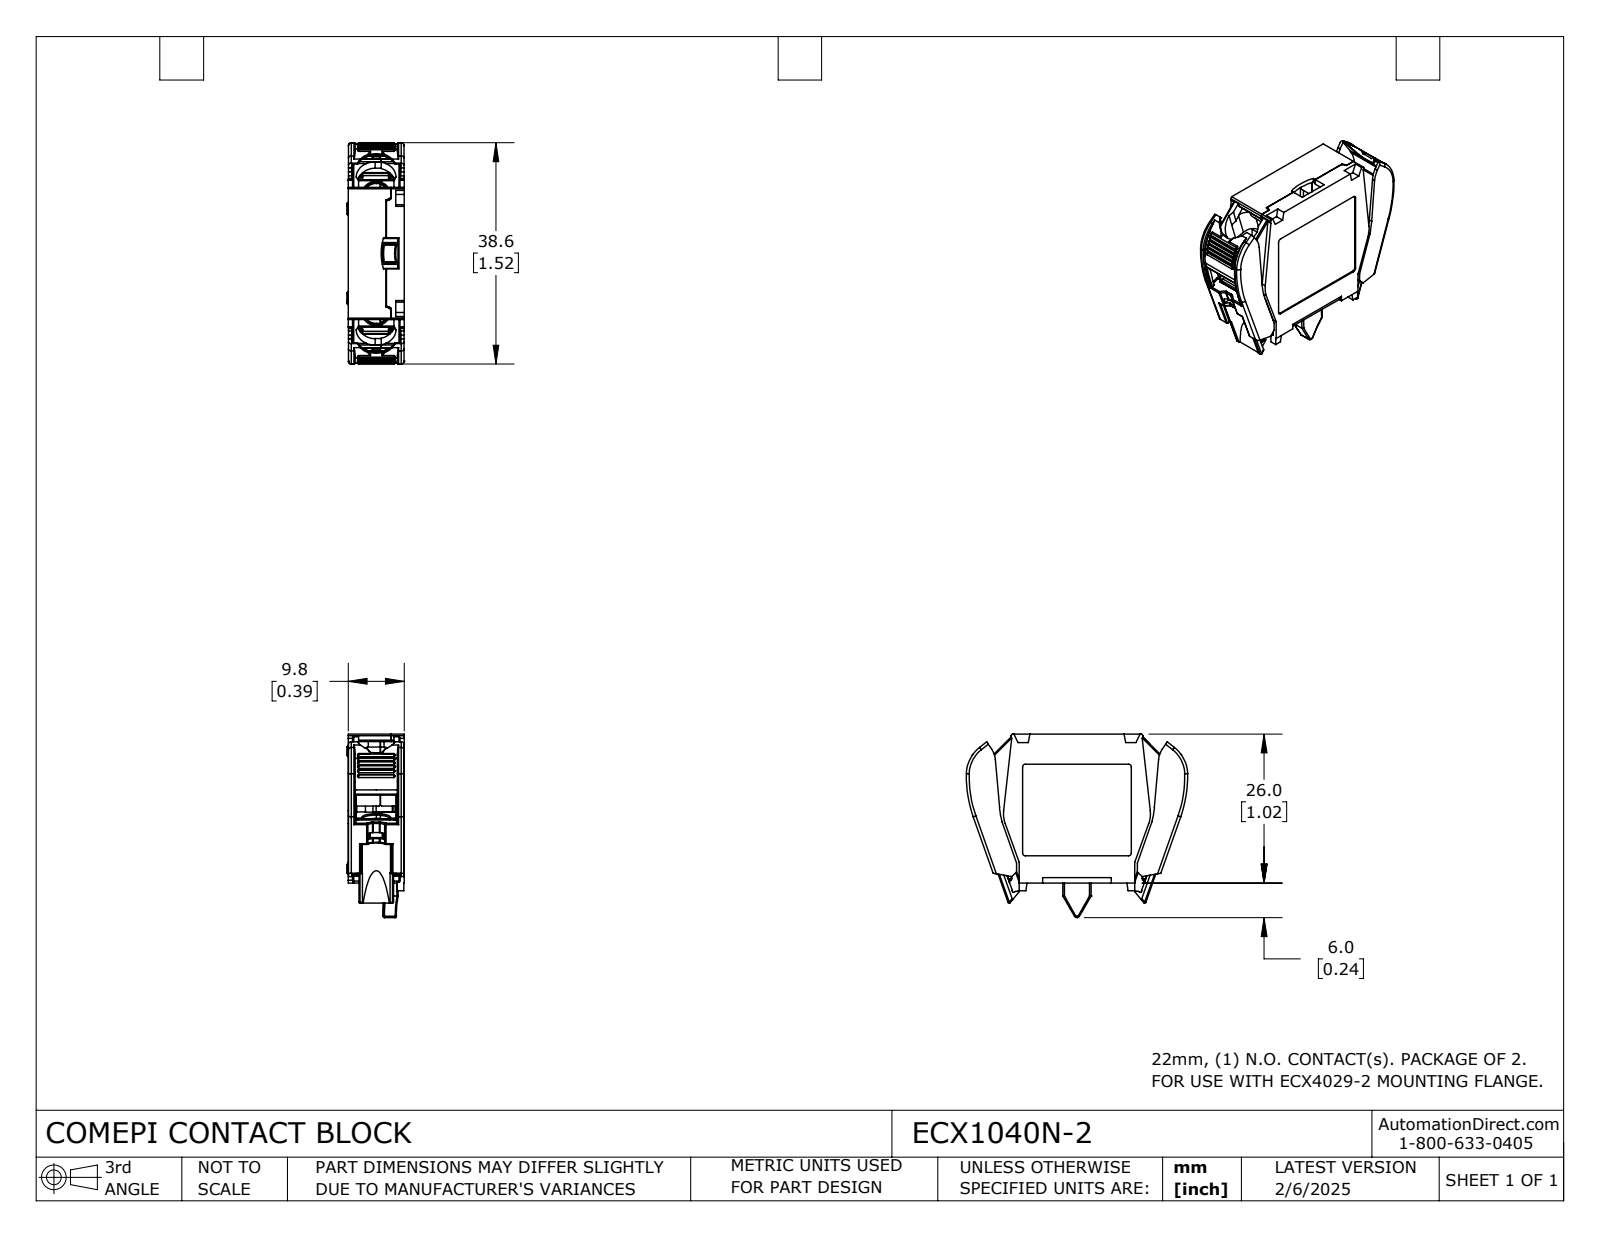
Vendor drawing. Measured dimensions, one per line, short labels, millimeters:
name: ECX1040N-2
written by: SolidWorks 2024 (CONFIG_CONTROL_DESIGN)
unit: mm
bodies: 5 solids, 1545 faces (815 planar, 491 cylindrical, 239 other)
size: 38.6 × 32 × 10.1
volume: 4 030 mm³; area: 8 613 mm²
holes: 4× ⌀2, 4× ⌀2.4, 4× ⌀3
bosses: 4× ⌀2.4, 4× ⌀1.9
rounds: 109× R0.2, 24× R0.3, 18× R0.2, 16× R0.5, 14× R0.1, 12× R0.3, 10× R0.1, 10× R0.2
face distances: 0.7, 1.3, 8.1, 9.6, 0.8, 1.5, 8.3, 8.3, 8.2, 9.8
hole spacings: 20.5, 25.8, 15.2, 16
